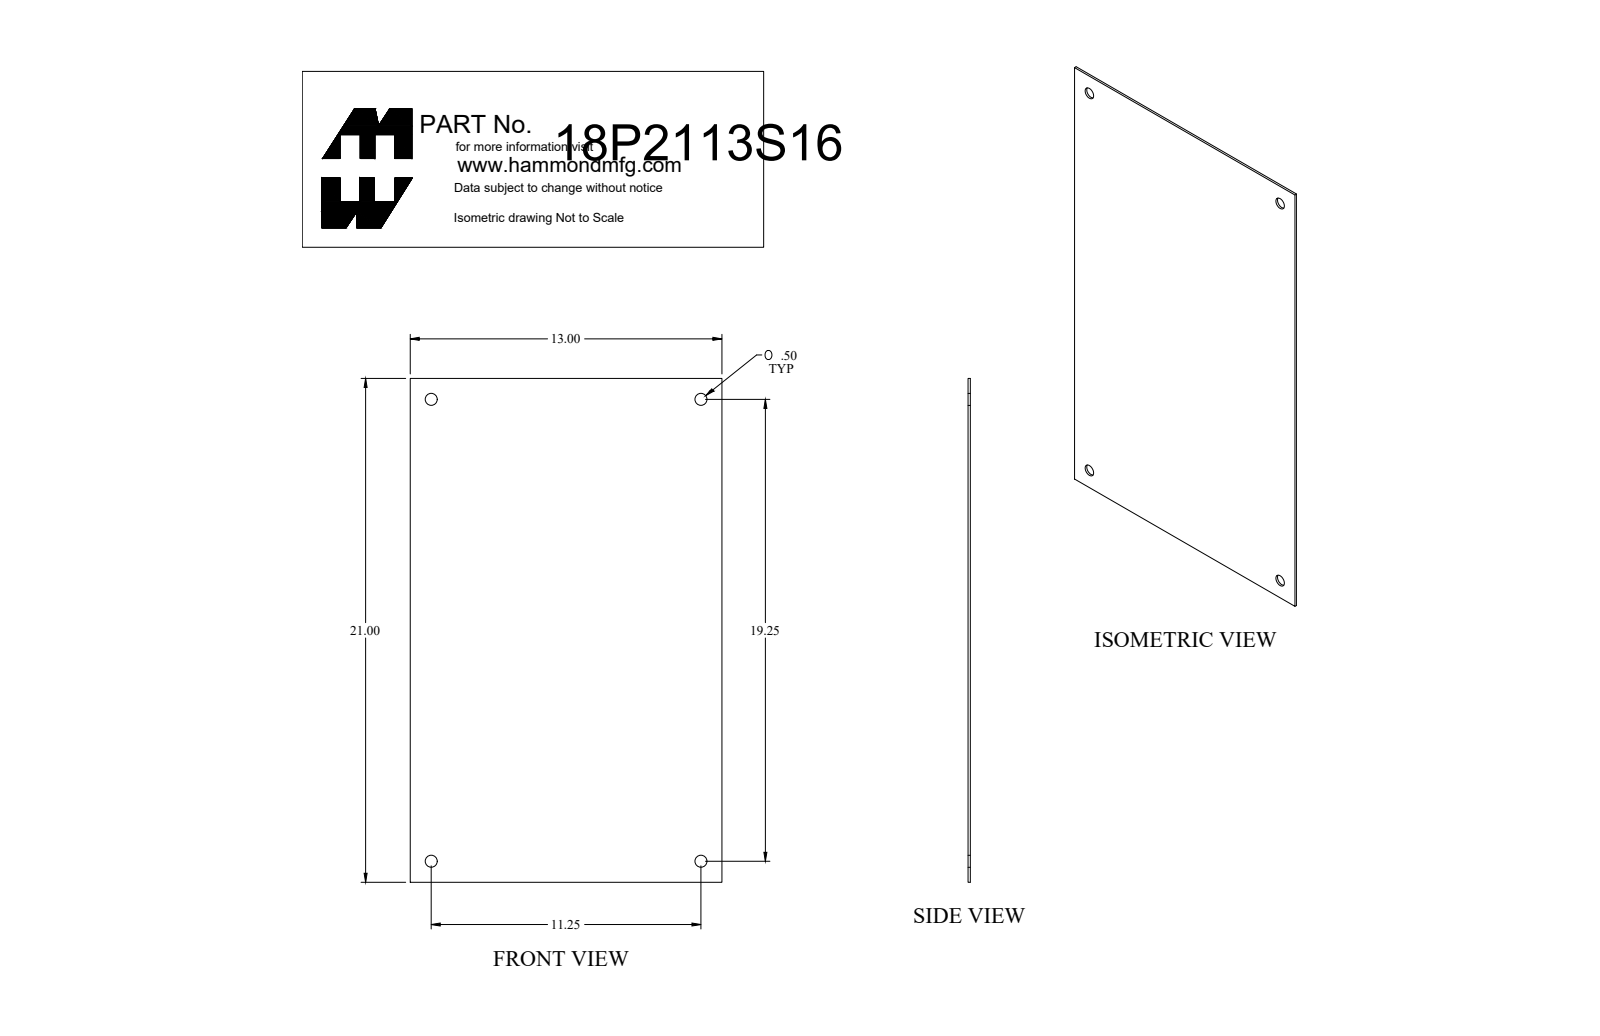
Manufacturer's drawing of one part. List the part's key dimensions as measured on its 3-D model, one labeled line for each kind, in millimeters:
Part name (STEP PRODUCT): 18P2113S16_Default
STEP written by: SolidWorks 2018 (CONFIG_CONTROL_DESIGN)
Units: millimetres
Bodies: 1 solid, 14 faces (6 planar, 8 cylindrical, 0 other)
Overall size (bounding box): 533.4 × 330.2 × 2.4
Volume: 423 800 mm³ · Surface area: 355 800 mm²
Round holes (diameter × count): ⌀12.7 ×4
Main face-to-face distances: 2.4, 330.2, 533.4
Hole centre spacings: 285.8, 489, 566.3
